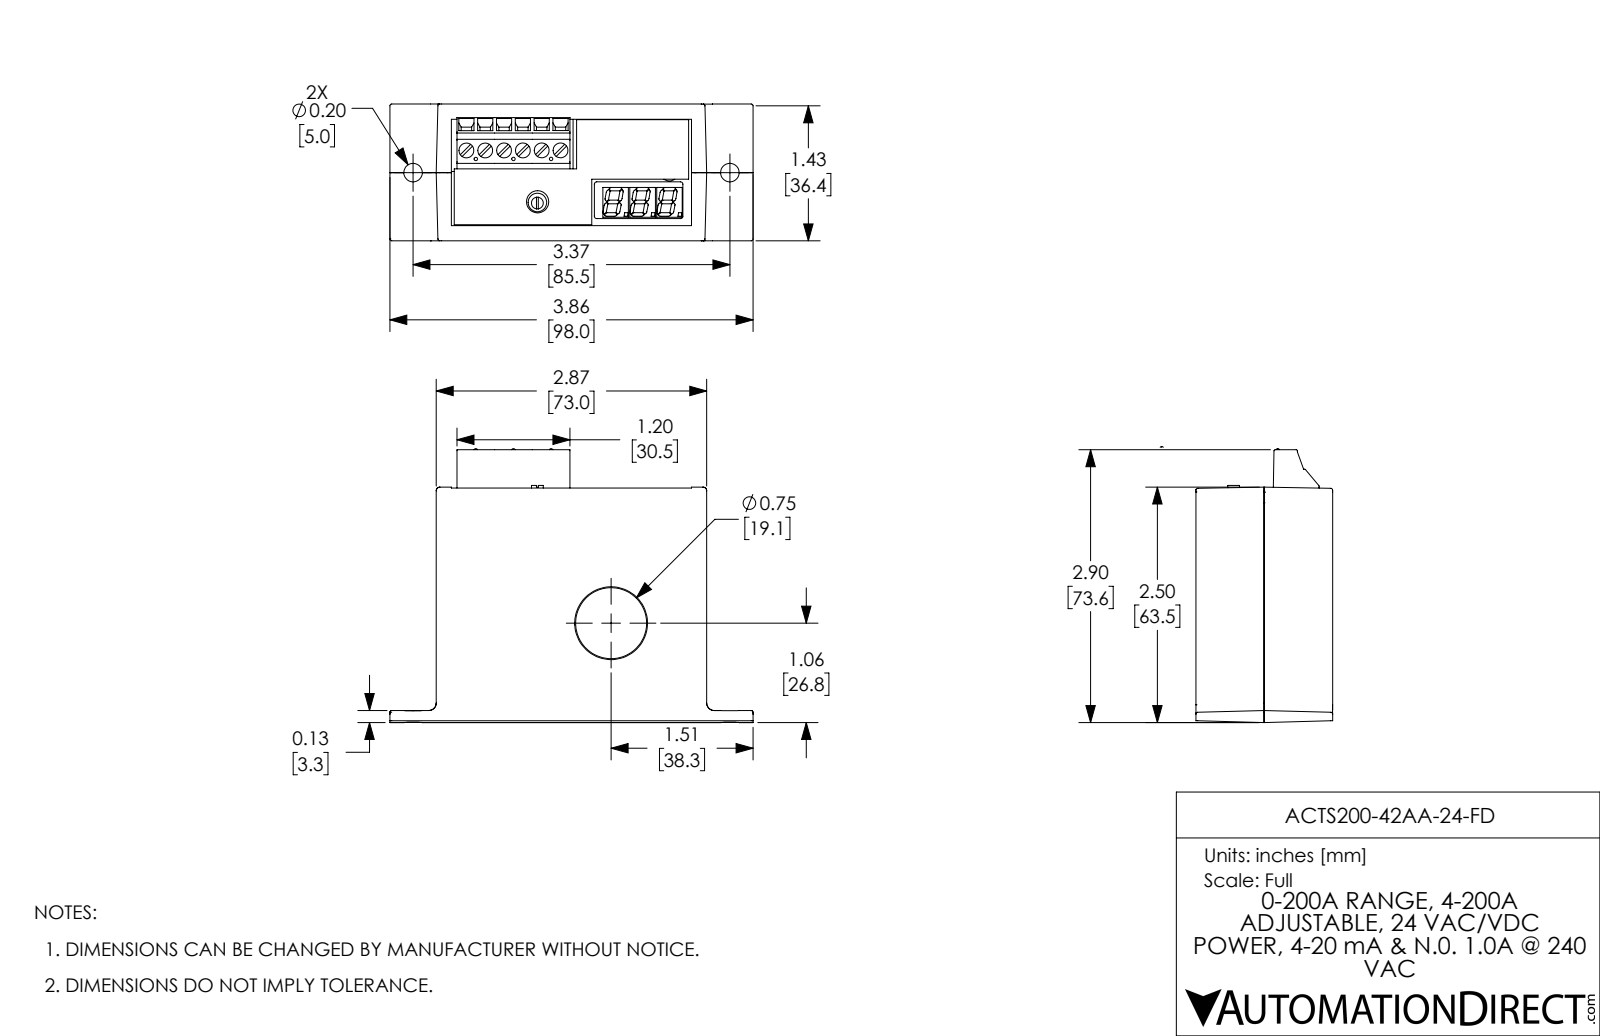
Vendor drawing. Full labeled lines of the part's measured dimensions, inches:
Part name (STEP PRODUCT): ACTS200-42AA-24-FD
STEP written by: SolidWorks 2017 (AUTOMOTIVE_DESIGN)
Units: inches
Bodies: 4 solids, 694 faces (498 planar, 113 cylindrical, 83 other)
Overall size (bounding box): 3.858 × 2.909 × 1.453
Volume: 9.871 in³ · Surface area: 71.12 in²
Round holes (diameter × count): ⌀0.157 ×6, ⌀0.197 ×5, ⌀0.059 ×4, ⌀0.26 ×2, ⌀0.154 ×1, ⌀0.198 ×1, ⌀0.236 ×1, ⌀0.774 ×1
Round bosses / shafts (diameter × count): ⌀0.126 ×1
Partial cylindrical surfaces — rounded edges, fillets, slot ends (radius × count): R0.02 ×18, R0.012 ×14, R0.025 ×5, R0.039 ×4, R0.079 ×4, R0.01 ×2, R0.077 ×2
Main face-to-face distances: 0.11, 1.343, 1.453, 2.874, 0.059, 0.069, 0.062, 0.072, 0.013, 0.072
Hole centre spacings: 0.2, 0.4, 0.697, 0.6, 0.37, 0.604, 0.789, 0.8
